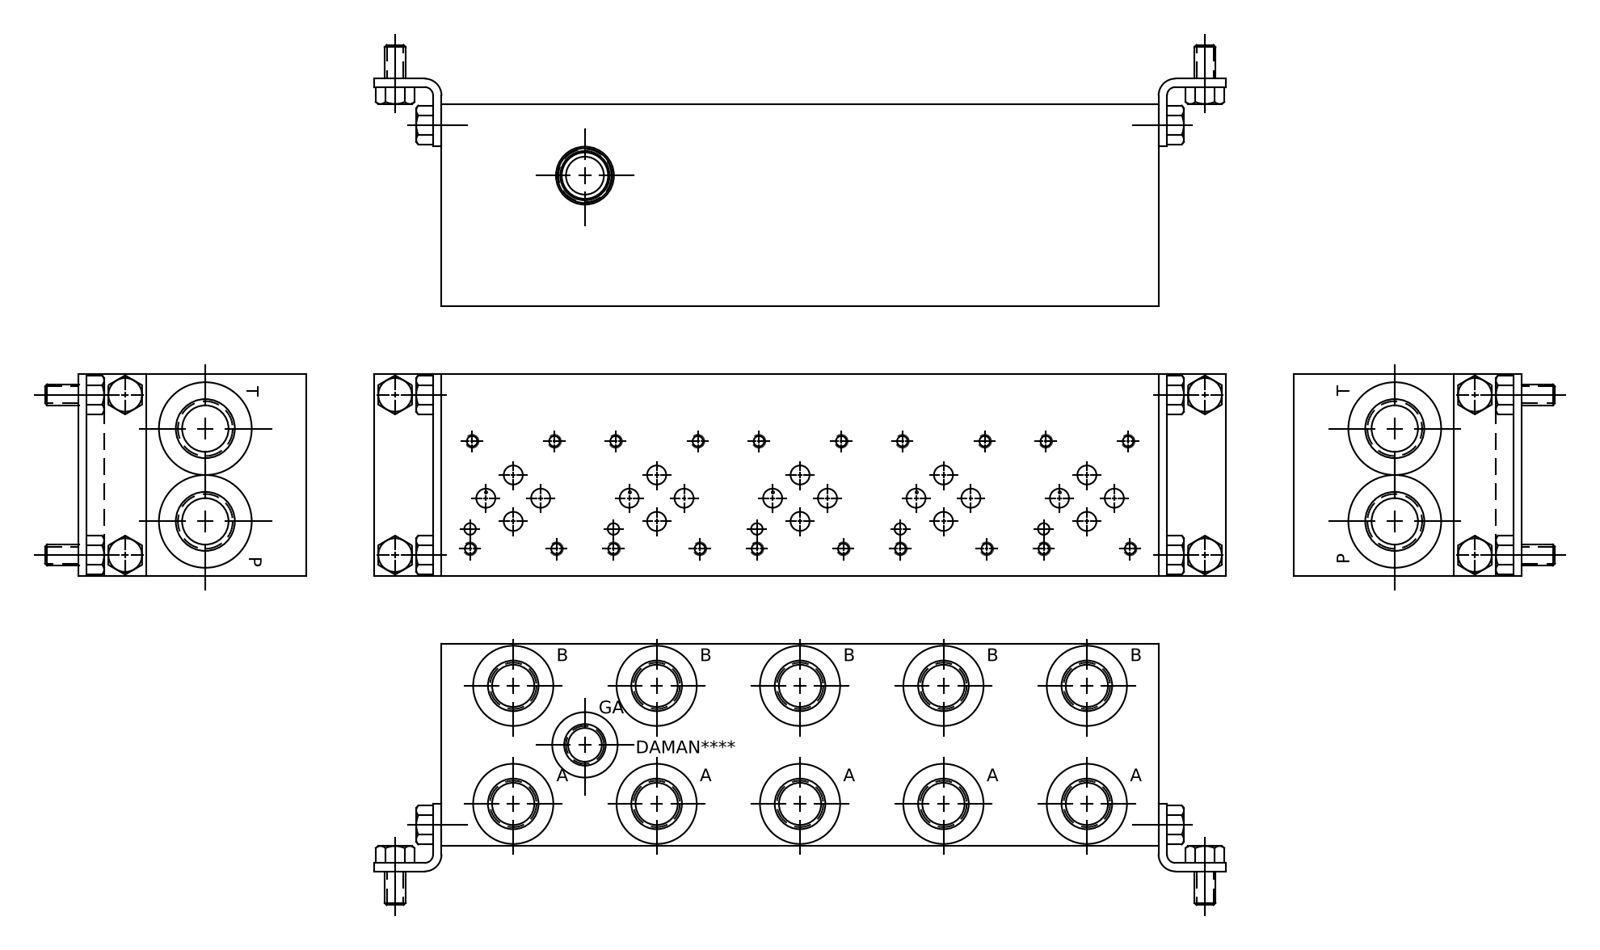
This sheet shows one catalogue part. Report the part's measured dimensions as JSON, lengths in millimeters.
{"part_name": "Part_AD03P052S_S_3D", "step_written_by": "Autodesk Inventor 2020 (AUTOMOTIVE_DESIGN)", "units": "millimeters", "bodies": {"solids": 1, "faces": 956, "planar": 467, "cylindrical": 154, "other": 335}, "overall_size": [270, 76.2, 76.2], "volume_mm3": 1431000, "surface_area_mm2": 126656, "round_holes": [[3.78, 20], [4.83, 20], [7.14, 15], [15.88, 10], [17.5, 10], [19.05, 10], [19.25, 10], [30.63, 10], [3.96, 5], [6.35, 5], [6.53, 2], [7.92, 2]], "face_to_face_distances": [76.2, 0.79, 75.41, 270, 269.21, 268.42, 14.27, 61.14, 15.06, 0.75], "hole_center_spacings": [54.1, 13.52, 107.95, 54.11, 108.21, 216.16, 12.99, 13.53]}
